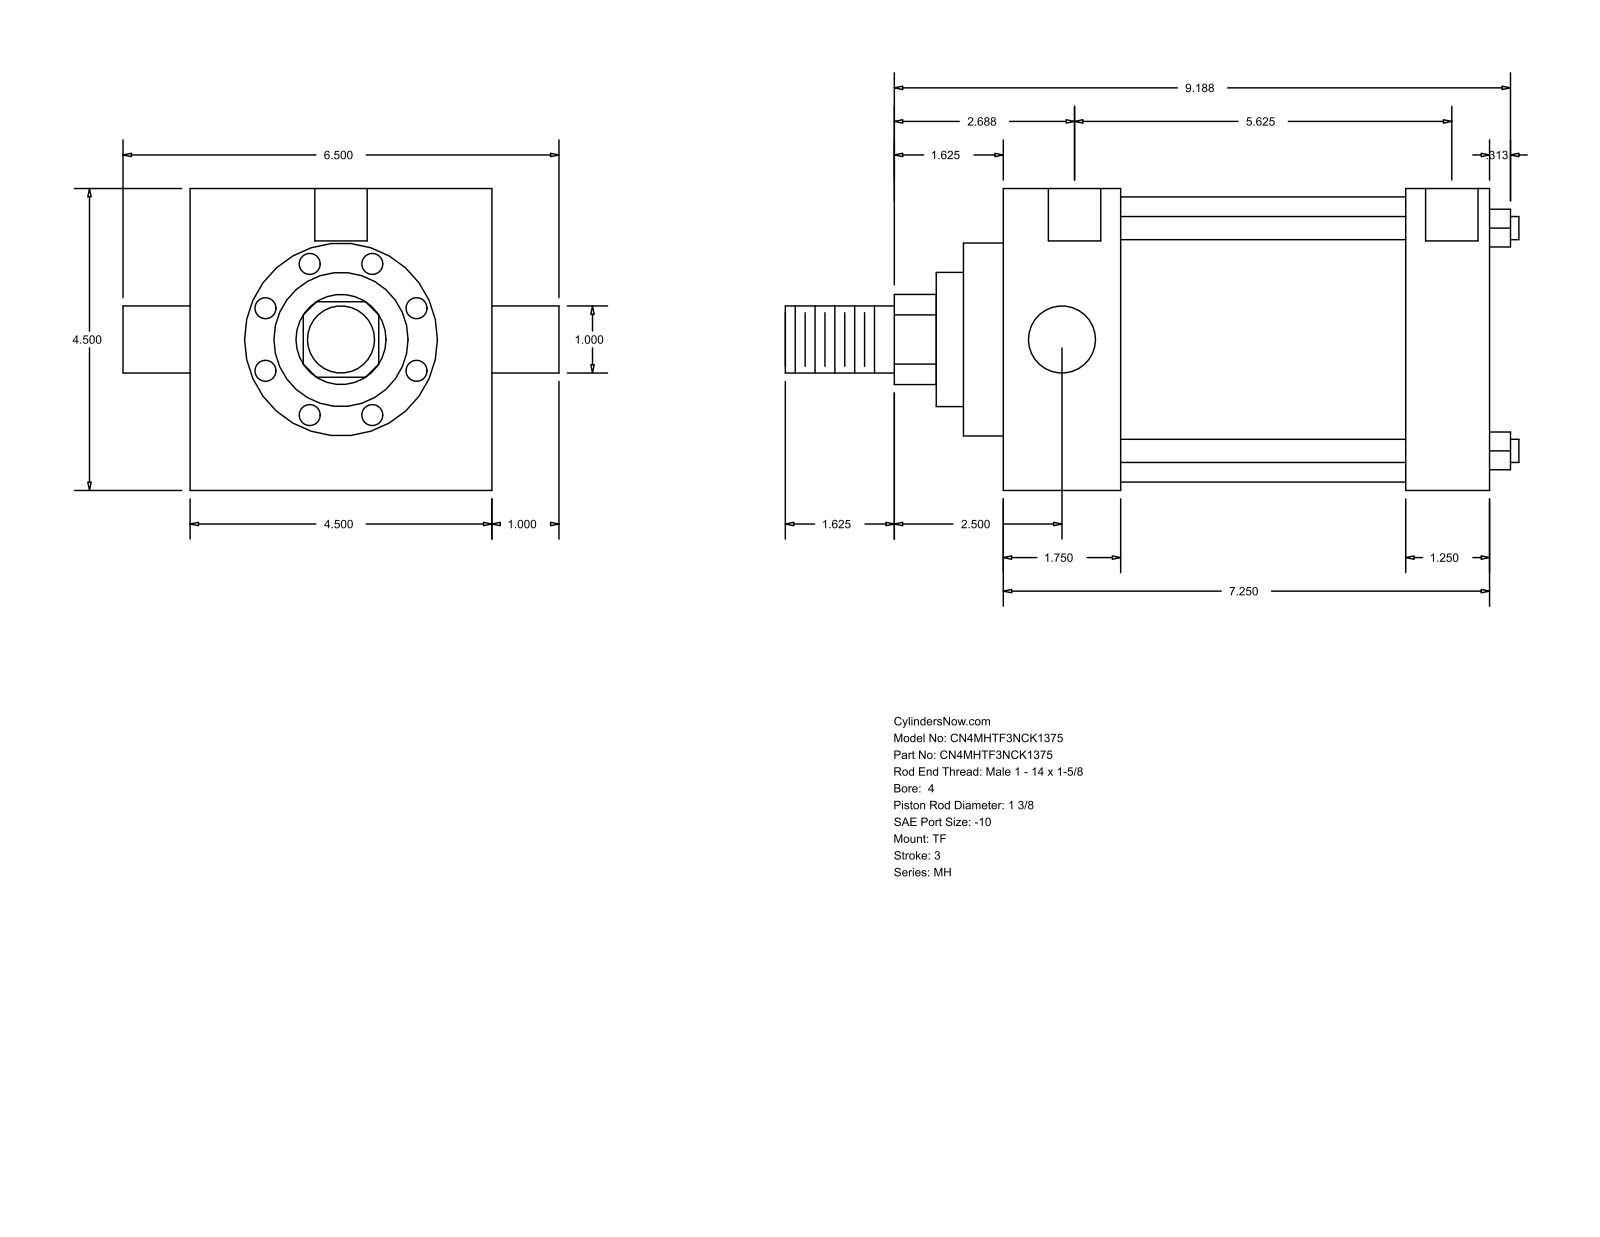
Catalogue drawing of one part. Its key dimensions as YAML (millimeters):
part_name: "MH_TF__0400_1.375"
step_written_by: "GSSL Pune (CONFIG_CONTROL_DESIGN)"
units: millimeters
bodies: {solids: 0, faces: 86, planar: 61, cylindrical: 25, other: 0}
overall_size: [277.81, 165.1, 114.3]
round_holes:
  - {diameter: 8.73, count: 3}
  - {diameter: 19.84, count: 2}
round_bosses_or_shafts:
  - {diameter: 8.76, count: 4}
  - {diameter: 25.4, count: 2}
  - {diameter: 107.95, count: 1}
  - {diameter: 73.03, count: 1}
  - {diameter: 50.8, count: 1}
  - {diameter: 34.92, count: 1}
partial_cylinders:
  - {radius: 17.06, count: 1}
face_to_face_distances: [114.3, 184.16, 44.45, 139.71, 152.41, 107.96, 31.75, 15.08, 59.53, 167.49]
hole_center_spacings: [1.58, 1.59, 142.88, 144.46, 144.47, 146.05]
